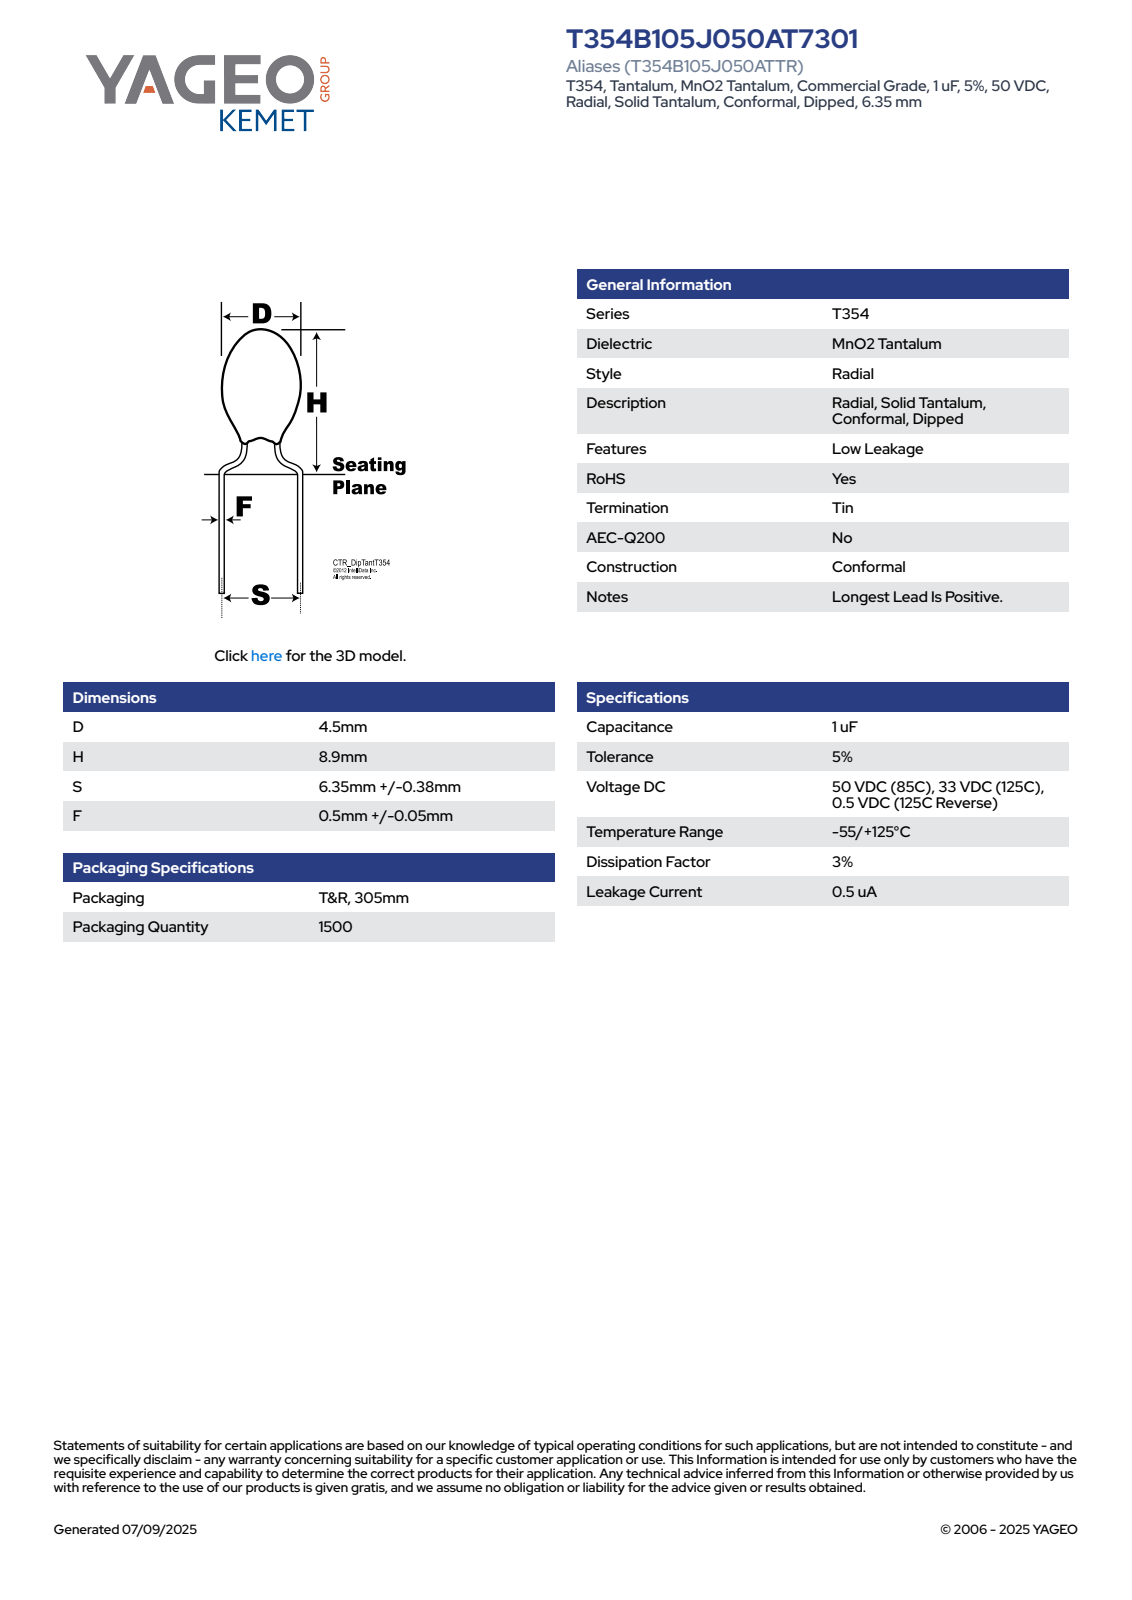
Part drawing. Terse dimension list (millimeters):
name: CTR_T354_D4.5H8.9S6.35LL5.56F0.55
written by: SolidWorks 2014 (AUTOMOTIVE_DESIGN)
unit: mm
bodies: 1 solid, 81 faces (26 planar, 10 cylindrical, 45 other)
size: 14.46 × 6.9 × 4.5
volume: 94 mm³; area: 137 mm²
bosses: 2× ⌀0.55, 1× ⌀4.5
rounds: 1× R2.24
face distances: 6.21, 8.25, 14.46, 12.33, 4.08, 2.13, 11.53, 3.28, 0.8, 2.93
